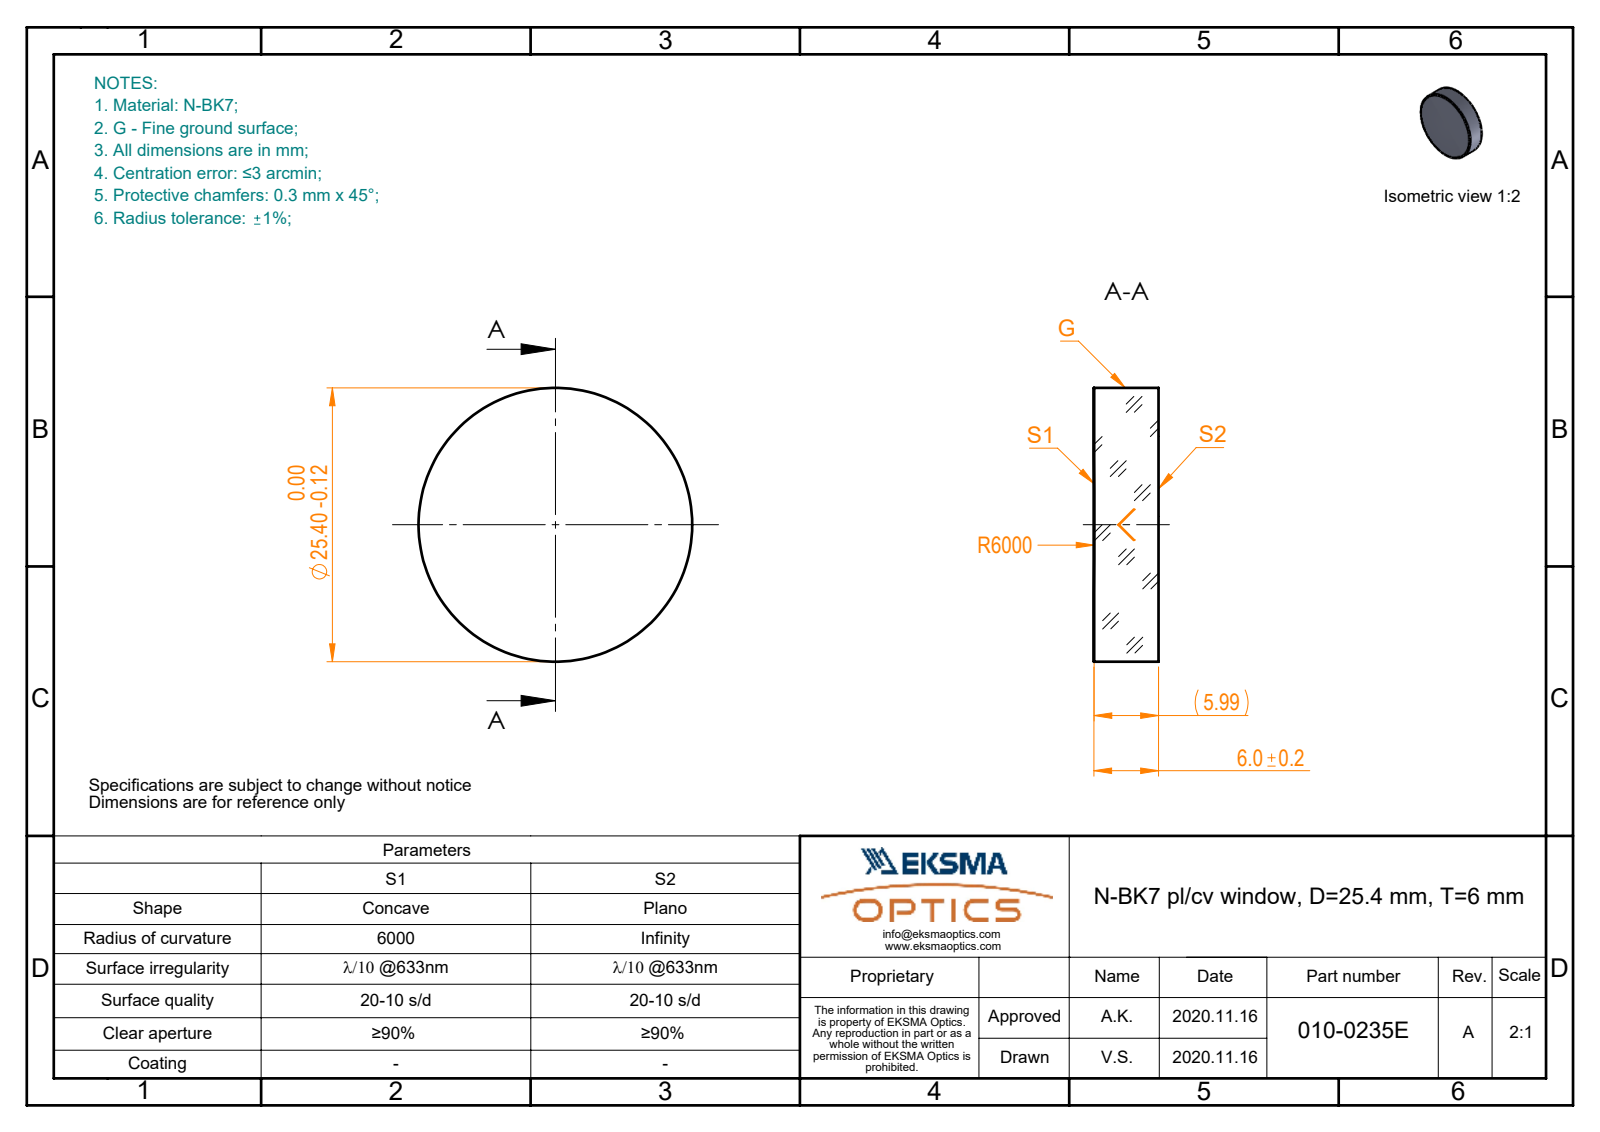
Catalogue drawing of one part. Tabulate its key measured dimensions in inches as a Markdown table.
| quantity | value |
| --- | --- |
| part name | 010-0235E_N-BK7_PCV_window |
| STEP written by | SolidWorks 2019 (CONFIG_CONTROL_DESIGN) |
| units | inches |
| bodies | 1 solid, 5 faces (1 planar, 2 cylindrical, 2 other) |
| overall size | 1 × 1 × 0.236 |
| volume | 0.185 in³ |
| surface area | 2.313 in² |
| round bosses / shafts (diameter × count) | 1 × 1 |
